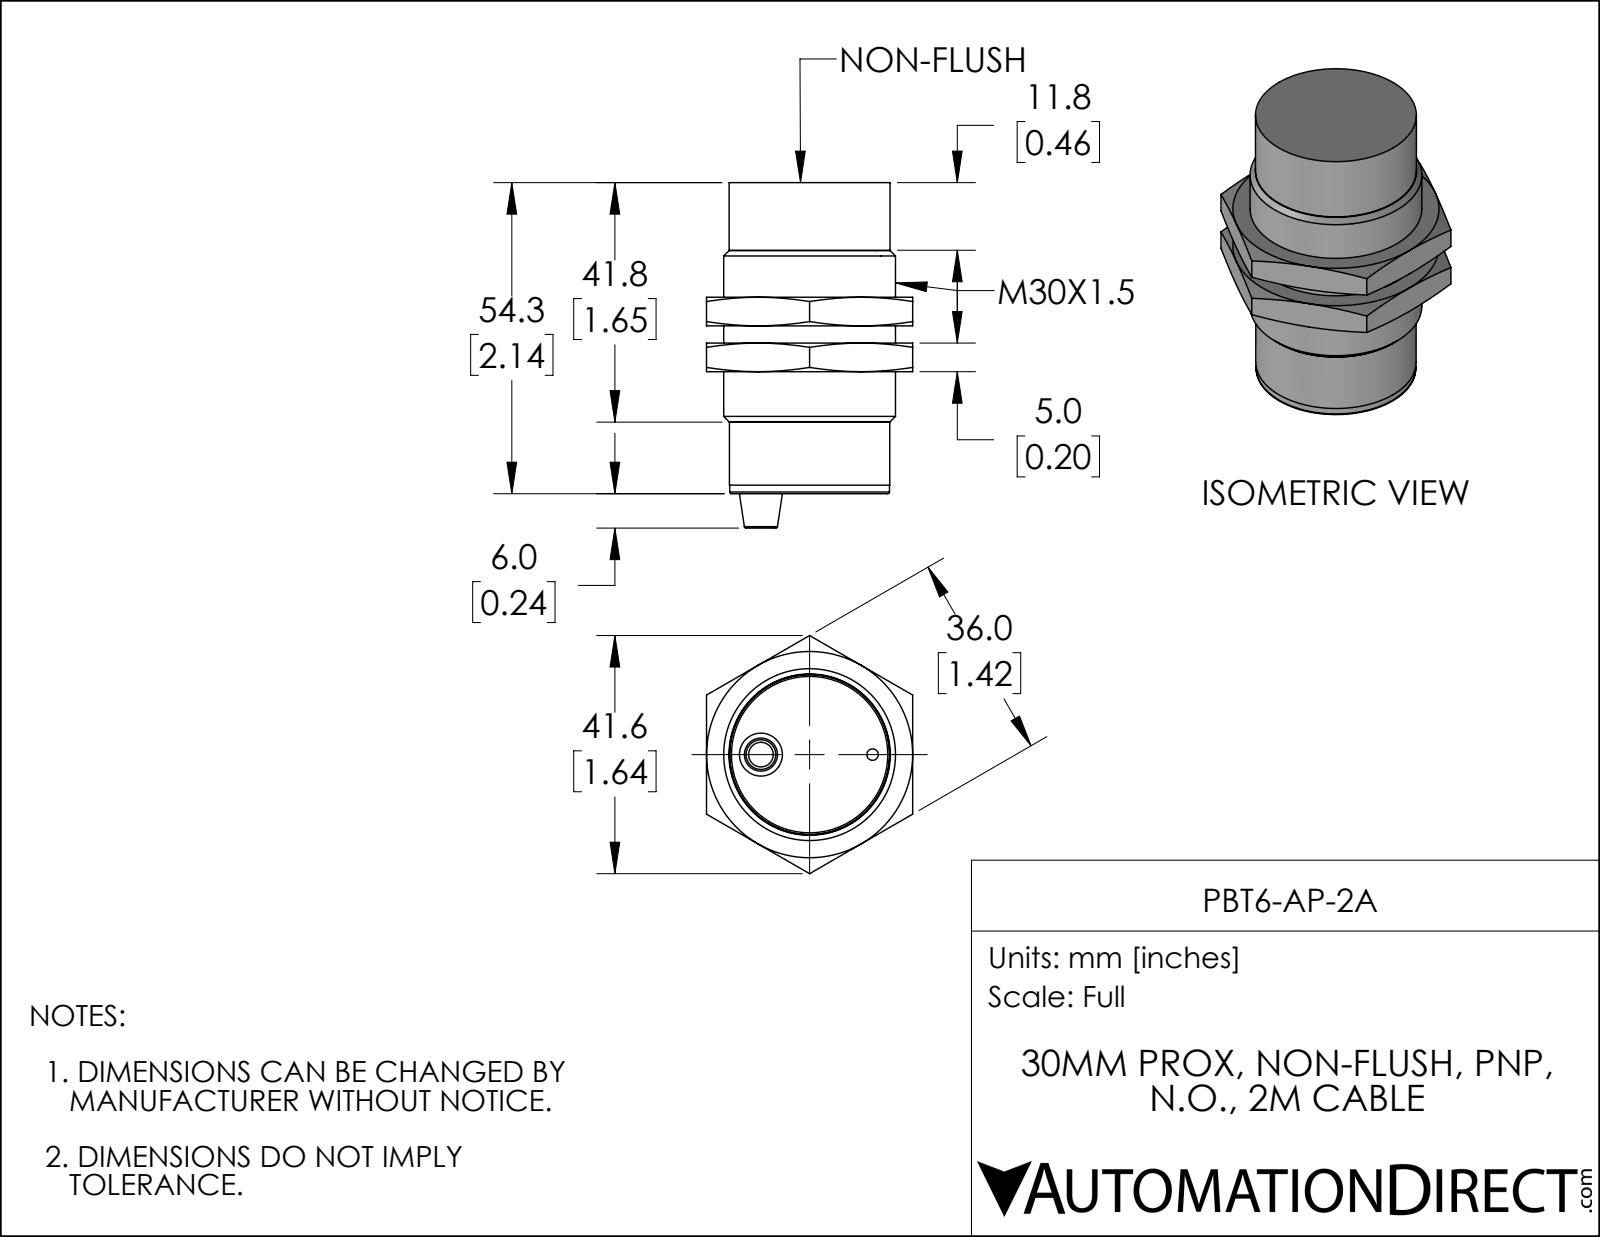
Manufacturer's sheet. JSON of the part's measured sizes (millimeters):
{"part_name": "DSD-0299", "step_written_by": "SolidWorks 2019 (AUTOMOTIVE_DESIGN)", "units": "millimeters", "bodies": {"solids": 1, "faces": 20, "planar": 7, "cylindrical": 6, "other": 7}, "overall_size": [60.3, 30, 30], "volume_mm3": 36220, "surface_area_mm2": 6471, "round_holes": [[2, 1], [4.3, 1]], "round_bosses_or_shafts": [[30, 1], [28.1, 1], [28, 1], [27.9, 1]], "face_to_face_distances": [54.3, 53.3, 1, 60.3, 7, 6, 11.8, 41.5, 42.5, 48.5], "hole_center_spacings": [19.5]}
